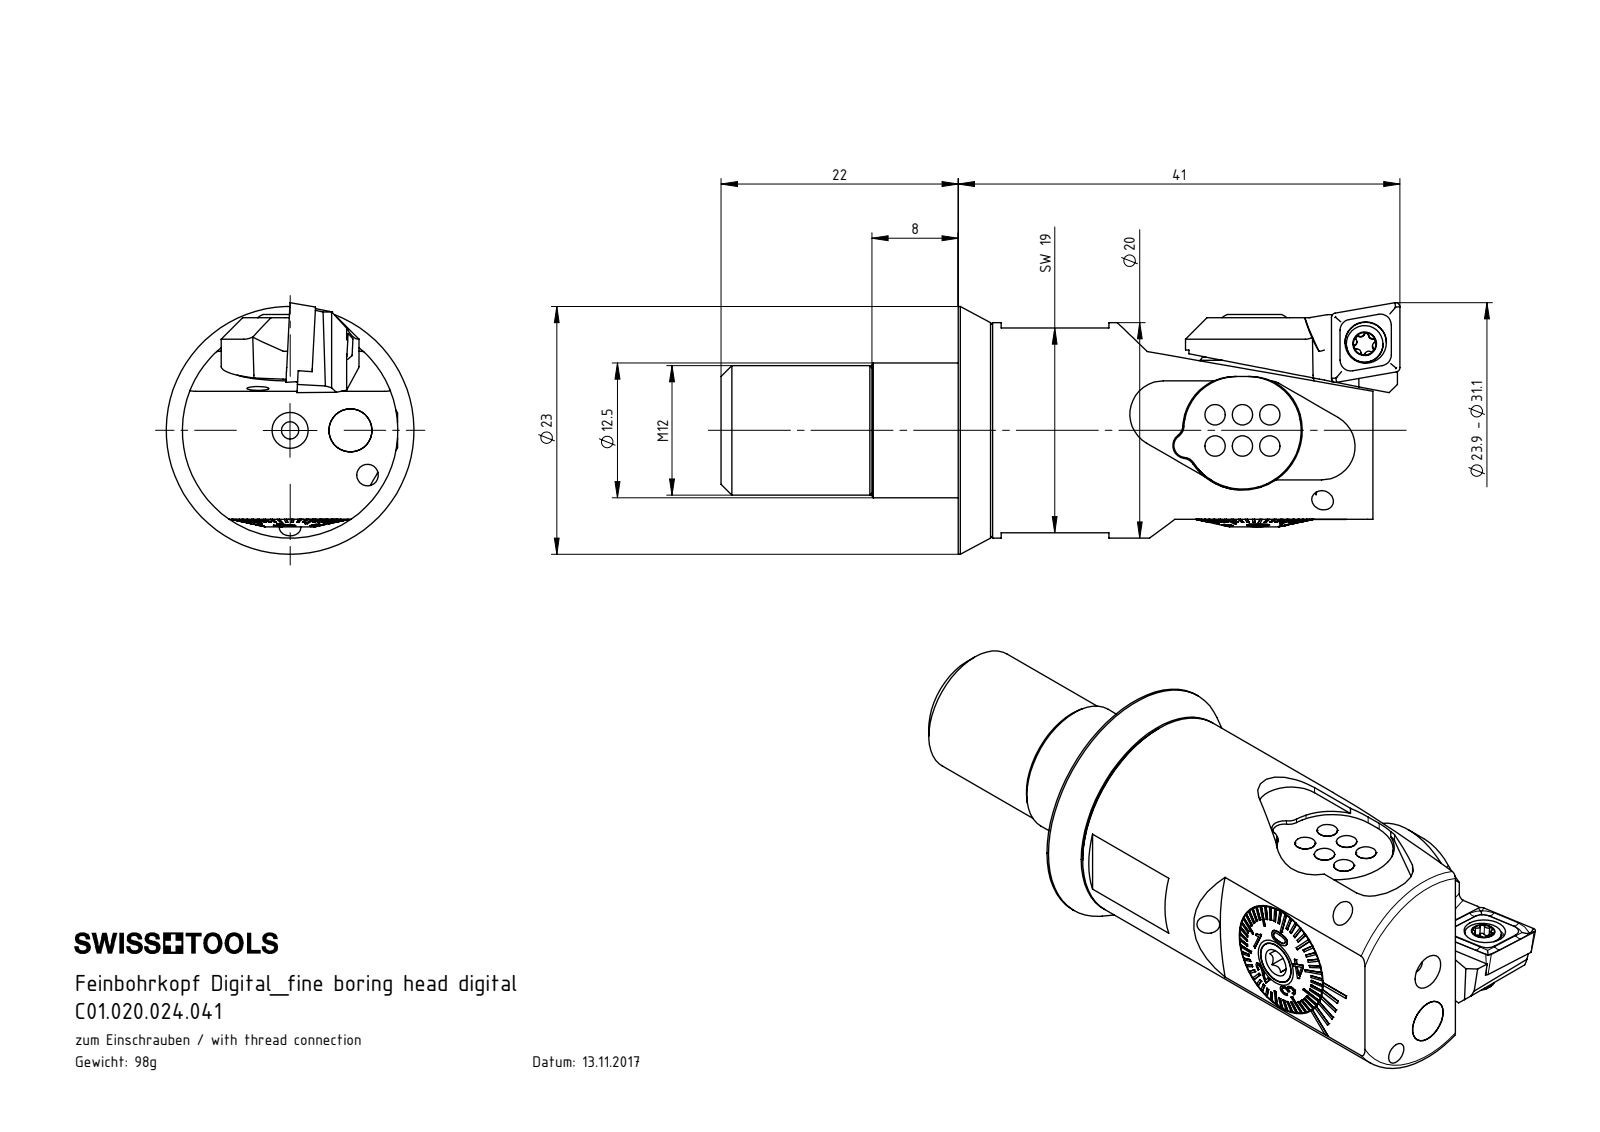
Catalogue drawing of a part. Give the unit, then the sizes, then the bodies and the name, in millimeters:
Units: millimetres
Overall size (bounding box): 63 × 23.35 × 23
Round holes (diameter × count): ⌀2 ×5, ⌀3.3 ×3, ⌀0.7 ×1, ⌀1.6 ×1, ⌀1.9 ×1, ⌀2.05 ×1, ⌀2.4 ×1, ⌀2.5 ×1, ⌀2.8 ×1, ⌀3 ×1, ⌀3.85 ×1, ⌀4 ×1
Round bosses / shafts (diameter × count): ⌀1.9 ×6, ⌀6 ×2, ⌀4 ×2, ⌀3.95 ×2, ⌀23 ×1, ⌀20 ×1, ⌀12 ×1, ⌀10.98 ×1
Partial cylindrical surfaces — rounded edges, fillets, slot ends (radius × count): R0.21 ×6, R0.36 ×5, R1.1 ×3, R1.2 ×3, R5 ×3, R0.3 ×2, R0.5 ×2, R2 ×2
Main face-to-face distances: 3, 38.5, 35.5, 15.05, 8, 1.5, 11, 46.5, 6, 2.8
Hole centre spacings: 1.14, 2.6, 3.51, 4.44, 5.6, 8.3
Volume: 12 613 mm³ · Surface area: 10 313 mm²
Bodies: 18 solids, 883 faces (387 planar, 193 cylindrical, 303 other)
Part name (STEP PRODUCT): F20-BG2.008.009_A; F20-WCA.001.005_D_fertigbearbeitet; WCA-ER2.001.006_A; F20-BG2.007.006_A (+8 more)
STEP written by: SolidWorks 2017 (CONFIG_CONTROL_DESIGN)
